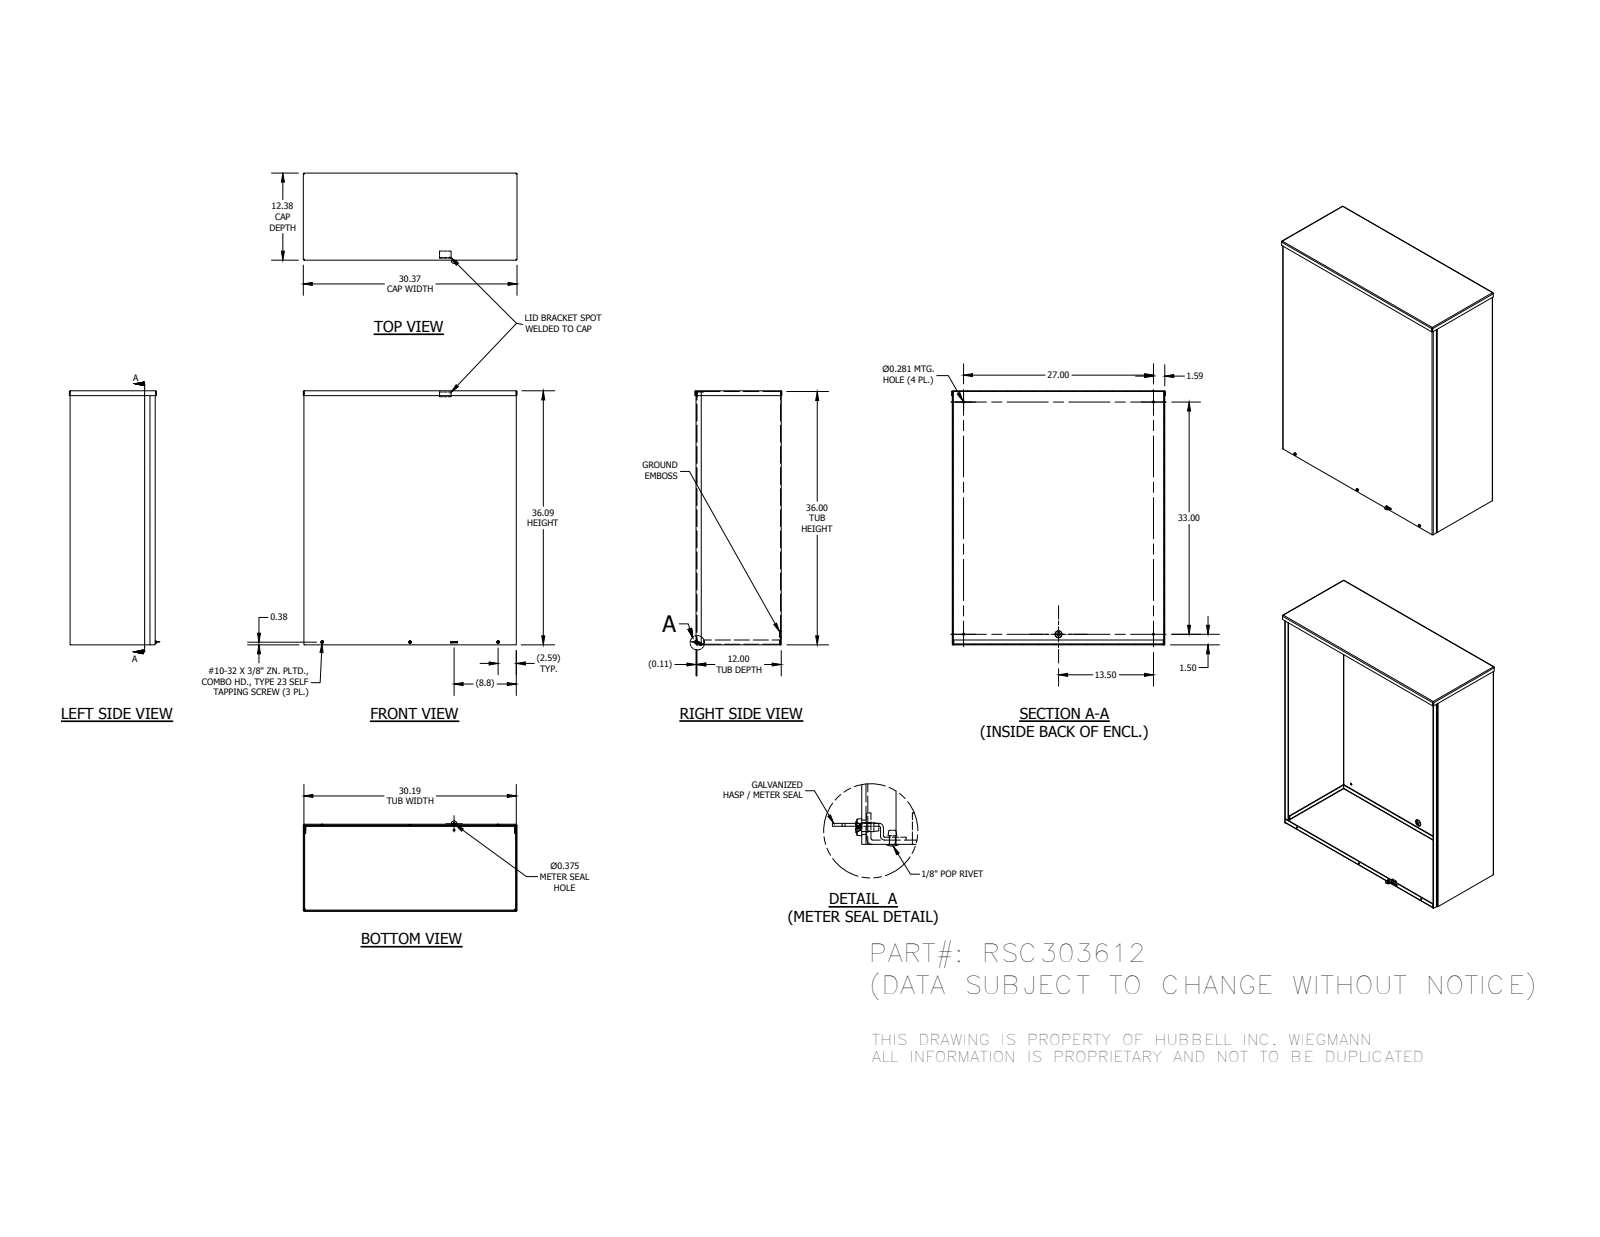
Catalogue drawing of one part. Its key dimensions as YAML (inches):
part_name: "RSC303612BKPA; RSC3012EWPA; RSC3036LFA; RSC3012CPA (+5 more)"
step_written_by: "Autodesk Inventor 2014 (AUTOMOTIVE_DESIGN)"
units: inches
bodies: {solids: 11, faces: 367, planar: 226, cylindrical: 64, other: 77}
overall_size: [36.134, 30.375, 12.844]
volume: 366
surface_area: 7865
round_holes:
  - {diameter: 0.313, count: 6}
  - {diameter: 0.171, count: 4}
  - {diameter: 0.281, count: 4}
  - {diameter: 0.125, count: 1}
  - {diameter: 0.136, count: 1}
  - {diameter: 0.375, count: 1}
round_bosses_or_shafts:
  - {diameter: 0.19, count: 3}
  - {diameter: 0.262, count: 1}
  - {diameter: 0.125, count: 1}
partial_cylinders:
  - {radius: 0.031, count: 19}
  - {radius: 0.125, count: 16}
  - {radius: 0.093, count: 2}
  - {radius: 0.105, count: 1}
  - {radius: 0.4, count: 1}
face_to_face_distances: [0.094, 12.016, 12.109, 11.922, 30.094, 36, 30.187, 30, 36.094, 35.906]
hole_center_spacings: [12.5, 13.547, 26.024, 25, 1.506, 12.55, 34.14, 36.698]
